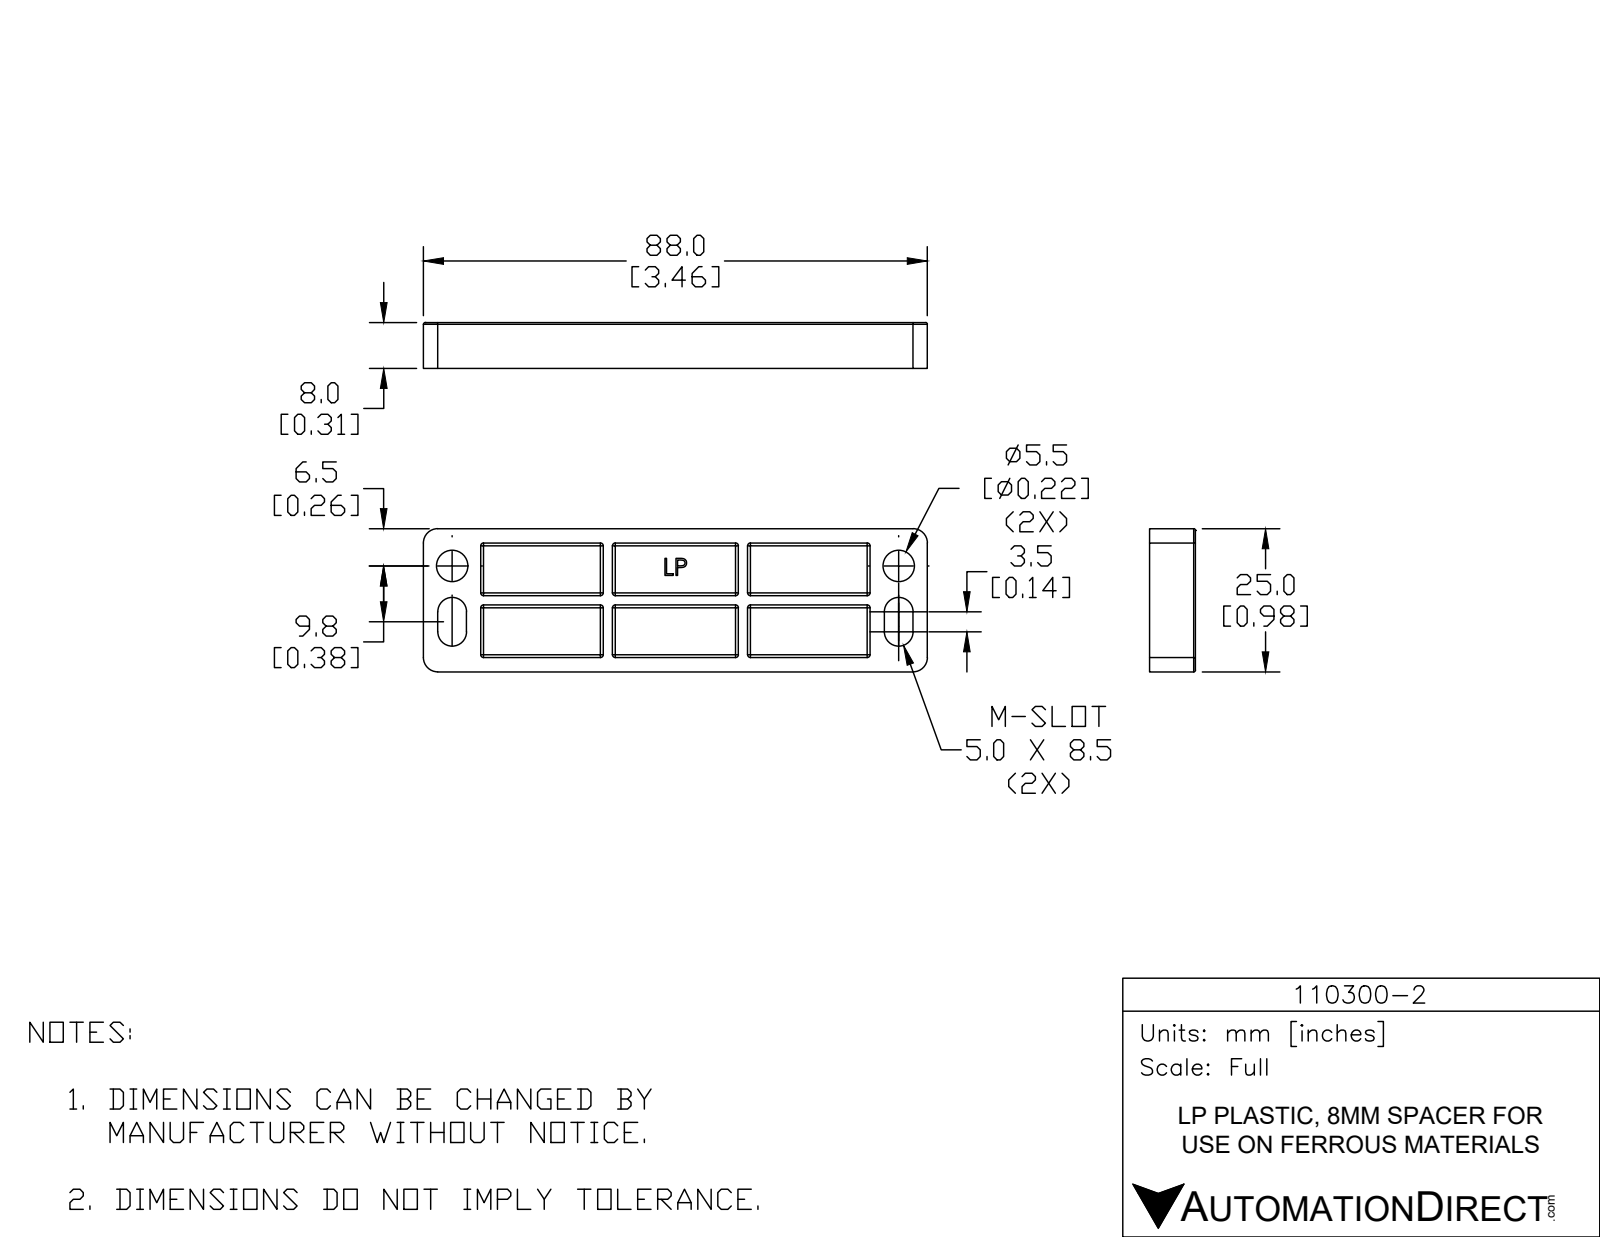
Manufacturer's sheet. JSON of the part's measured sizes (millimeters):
{"part_name": "110-LP Spacer", "step_written_by": "SolidWorks 2018 (CONFIG_CONTROL_DESIGN)", "units": "millimeters", "bodies": {"solids": 1, "faces": 167, "planar": 61, "cylindrical": 64, "other": 42}, "overall_size": [88, 25, 8], "volume_mm3": 10598, "surface_area_mm2": 8239, "round_holes": [[5.5, 2]], "partial_cylinders_radius": [[0.5, 34], [2.5, 8], [0.3, 4]], "face_to_face_distances": [3, 5, 8, 2.5, 25, 11.7, 13.3, 22.5, 9.2, 10.8], "hole_center_spacings": [78]}
